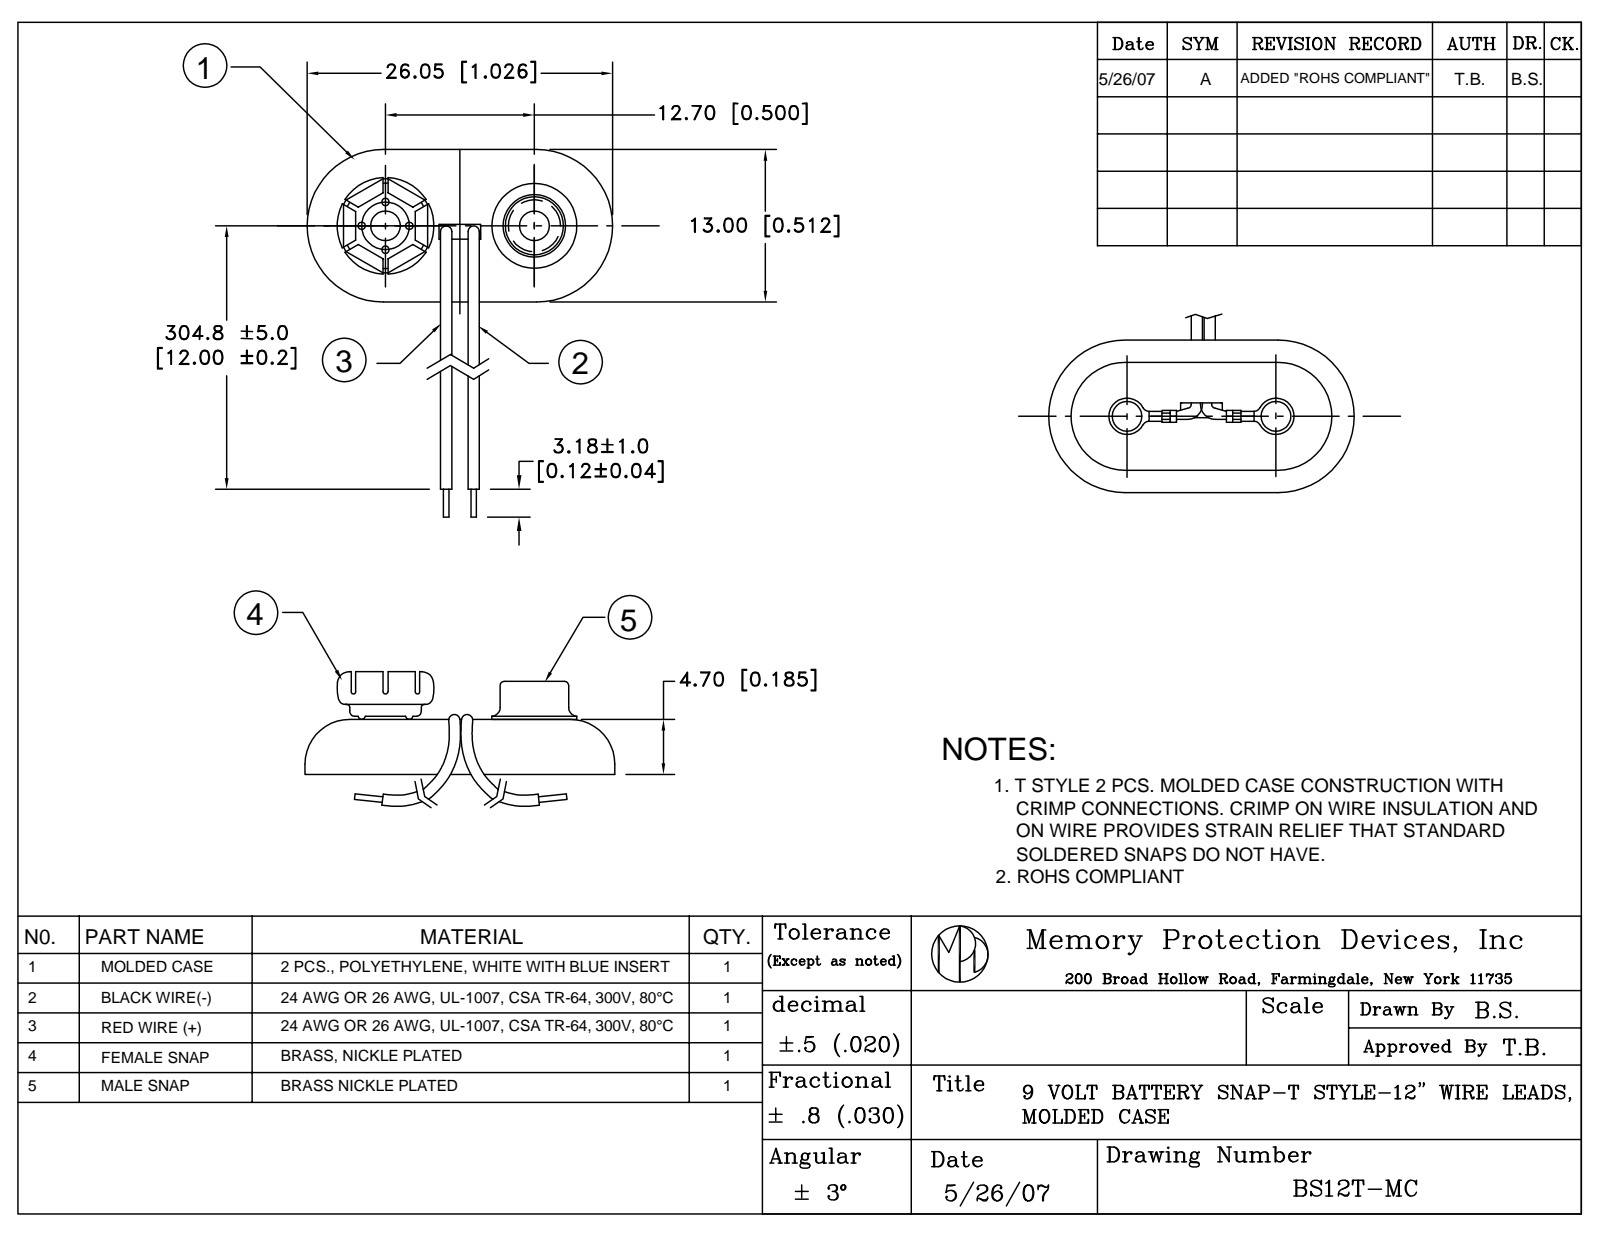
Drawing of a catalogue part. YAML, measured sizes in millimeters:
part_name: "BS12T-MC"
step_written_by: "SolidWorks 2017 (AUTOMOTIVE_DESIGN)"
units: millimeters
bodies: {solids: 7, faces: 163, planar: 81, cylindrical: 56, other: 26}
overall_size: [314.48, 26.05, 8.66]
volume: 2423
surface_area: 6235
round_holes:
  - {diameter: 0.6, count: 8}
  - {diameter: 2.5, count: 2}
  - {diameter: 2.63, count: 1}
  - {diameter: 4.44, count: 1}
  - {diameter: 7.3, count: 1}
round_bosses_or_shafts:
  - {diameter: 1.4, count: 4}
  - {diameter: 0.58, count: 2}
  - {diameter: 8, count: 1}
  - {diameter: 6.8, count: 1}
  - {diameter: 6, count: 1}
  - {diameter: 5.21, count: 1}
partial_cylinders:
  - {radius: 0.25, count: 6}
  - {radius: 2, count: 2}
  - {radius: 6.5, count: 2}
face_to_face_distances: [4.7, 1.5, 6.2, 13, 1.2, 0.9, 0.6, 1.8, 5.9, 5]
hole_center_spacings: [2.1, 2.97, 4.2, 3.02, 2.92, 2.93, 2.98, 12.87]
